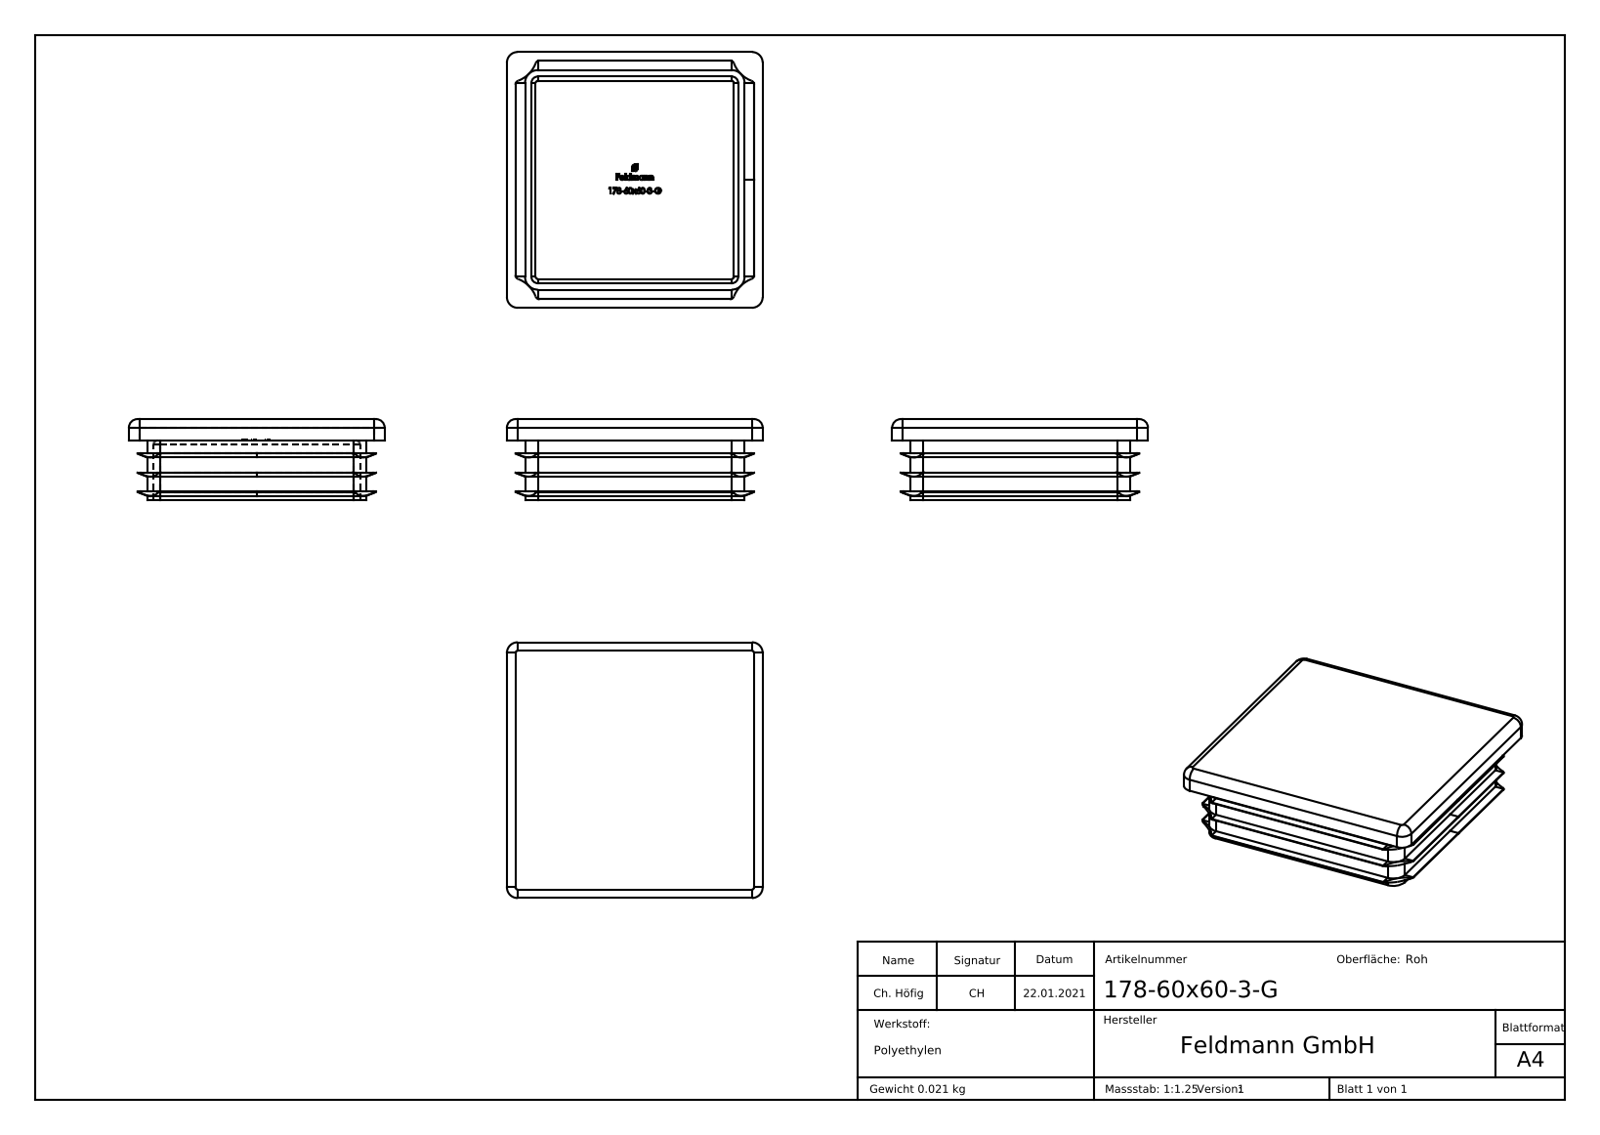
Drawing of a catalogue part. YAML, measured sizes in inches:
part_name: "178-60x60-3-G"
step_written_by: "SolidWorks 2018 (CONFIG_CONTROL_DESIGN)"
units: inches
bodies: {solids: 1, faces: 495, planar: 236, cylindrical: 83, other: 176}
overall_size: [2.362, 2.362, 0.748]
volume: 1.381
surface_area: 24.36
partial_cylinders:
  - {radius: 0.039, count: 12}
  - {radius: 0.059, count: 4}
  - {radius: 0.079, count: 4}
  - {radius: 0.098, count: 4}
  - {radius: 0.118, count: 4}
  - {radius: 0.276, count: 4}
face_to_face_distances: [0.197, 0.059, 1.969, 1.909, 2.028, 0.164, 0.177, 0.167, 0.226, 2.136]
